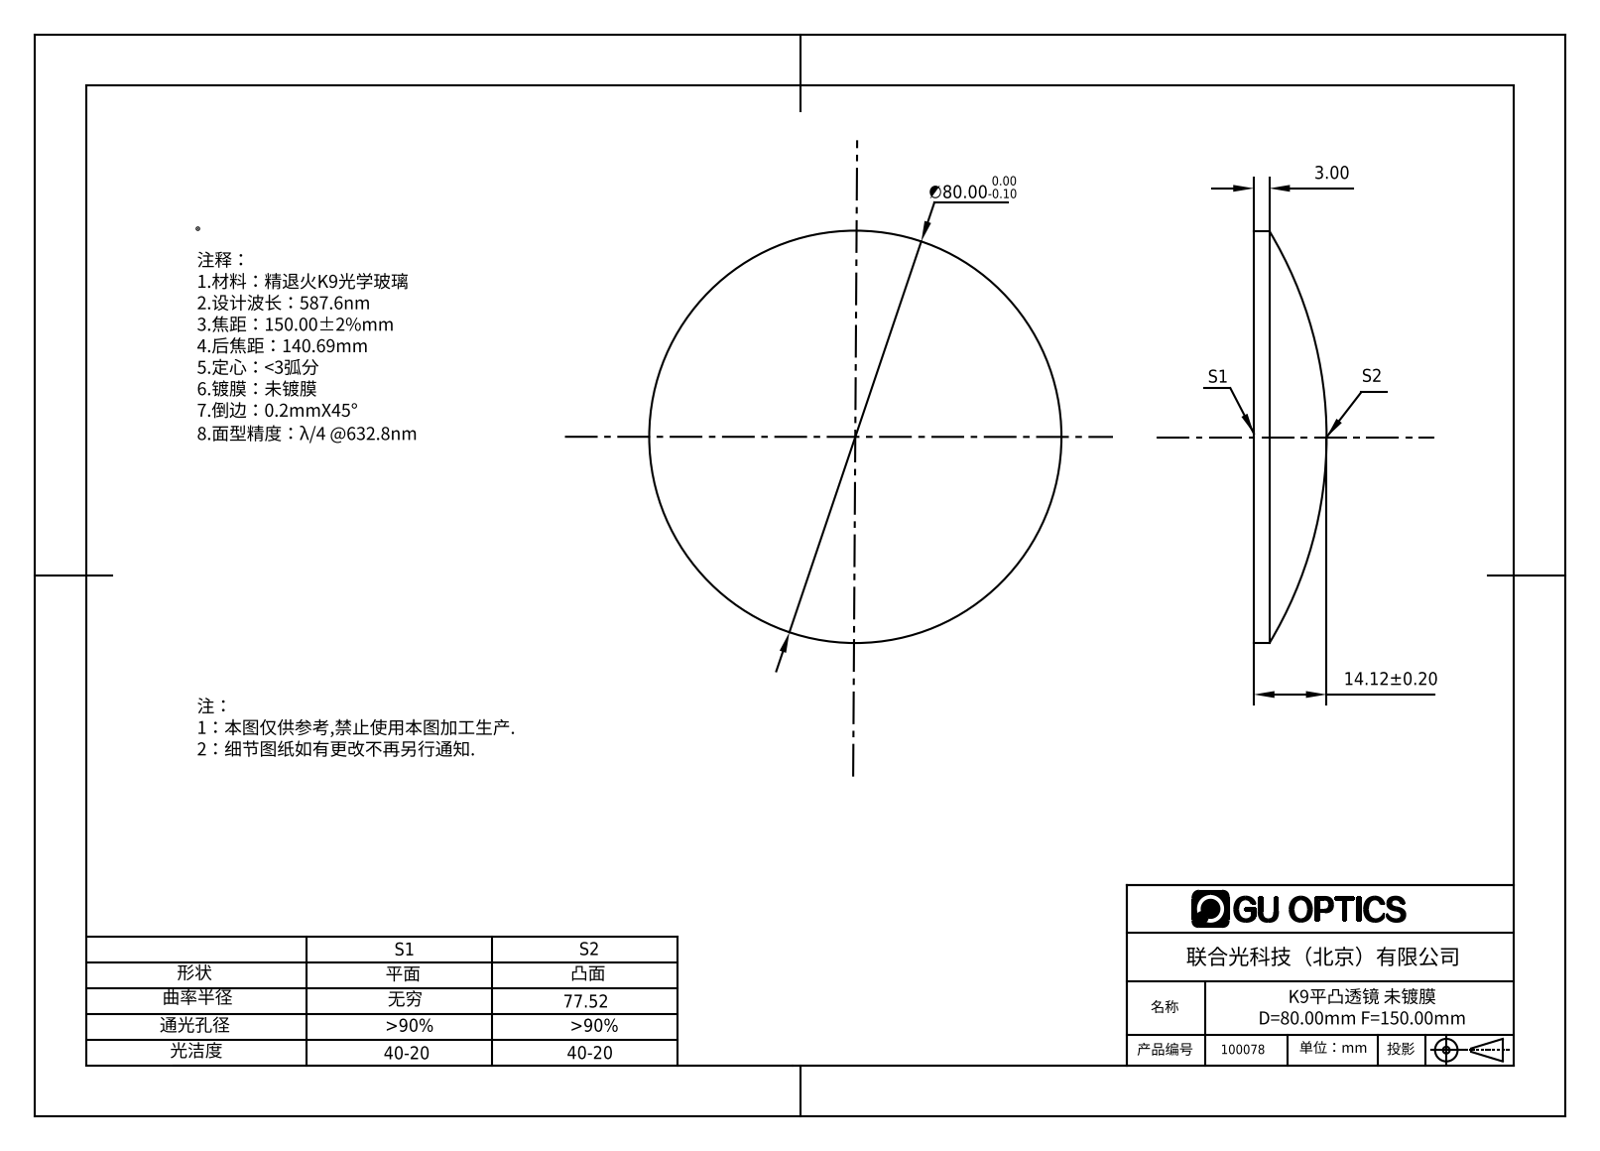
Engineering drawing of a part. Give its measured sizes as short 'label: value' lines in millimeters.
name: 100078
written by: SolidWorks 2016 (AUTOMOTIVE_DESIGN)
unit: mm
bodies: 1 solid, 5 faces (1 planar, 2 cylindrical, 2 other)
size: 80 × 80 × 14.12
volume: 43 747 mm³; area: 11 196 mm²
bosses: 1× ⌀80
